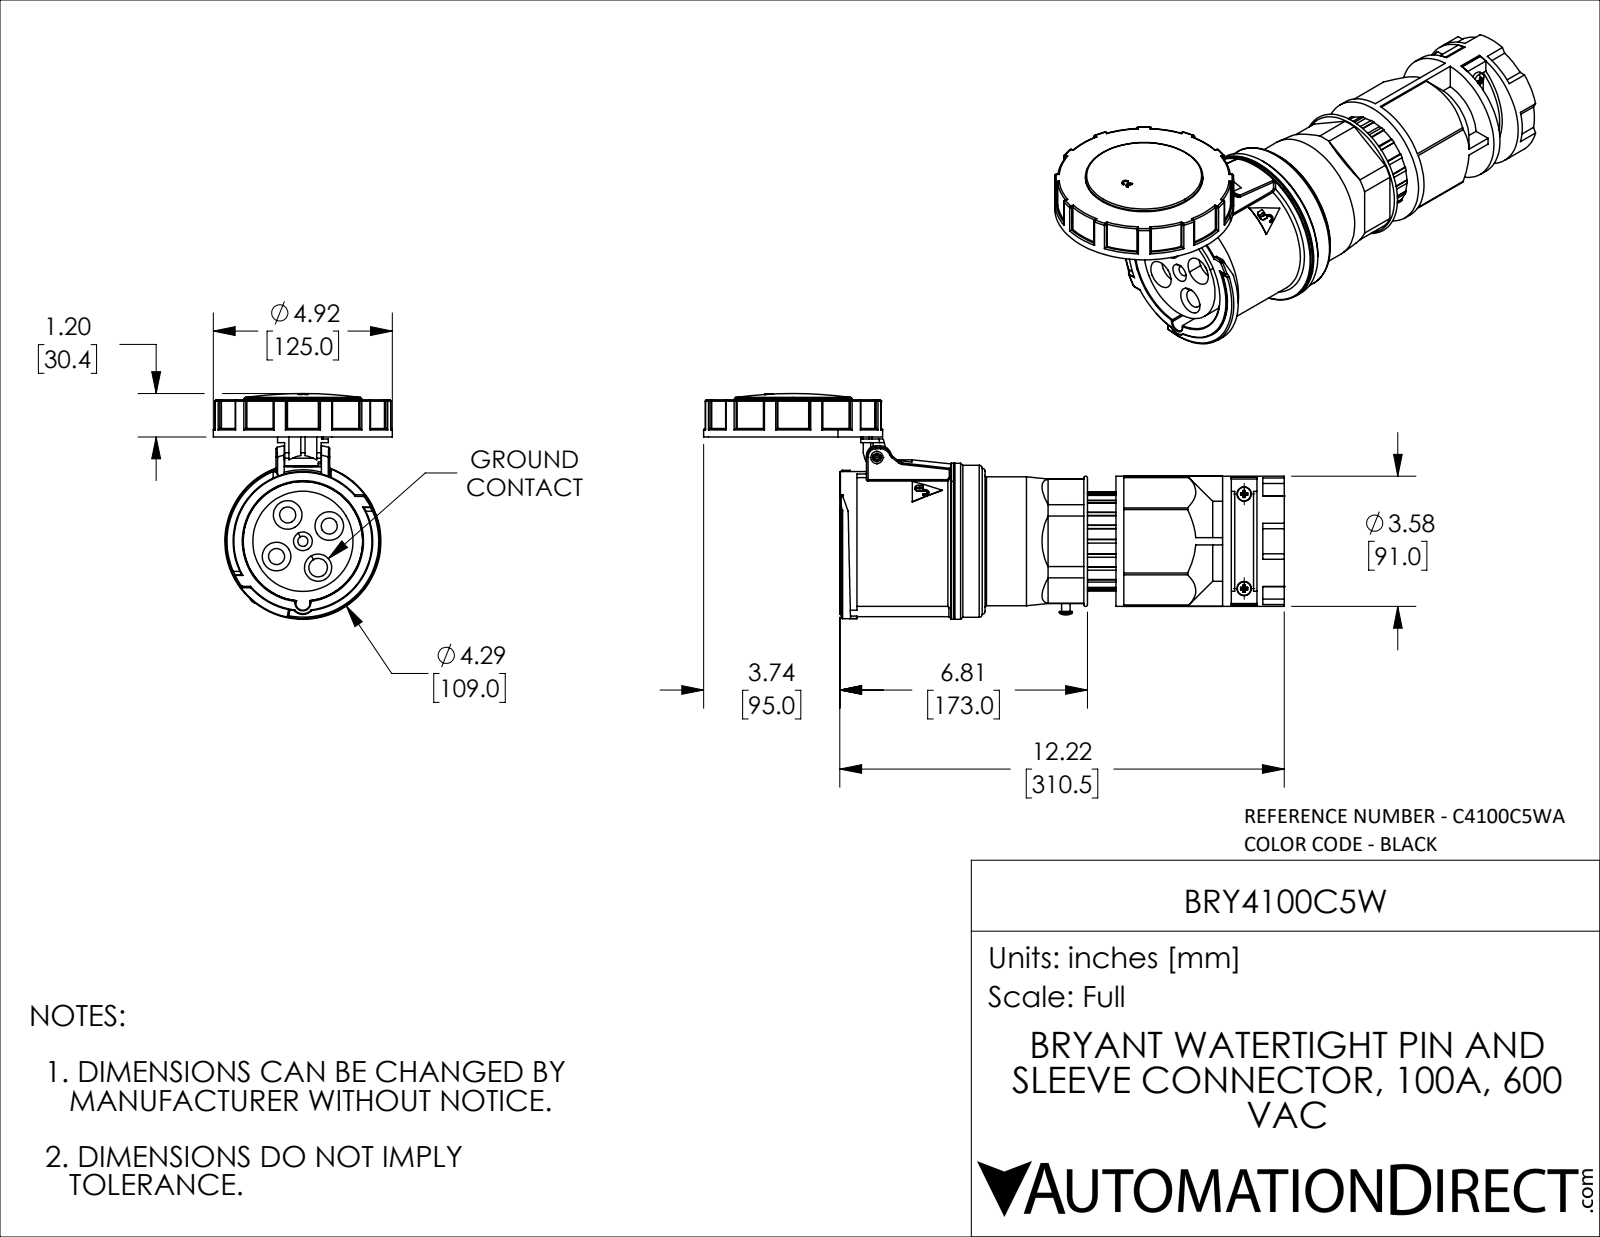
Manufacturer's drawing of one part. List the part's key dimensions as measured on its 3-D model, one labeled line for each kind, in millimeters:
Part name (STEP PRODUCT): BRY4100C5W
STEP written by: SolidWorks 2021 (CONFIG_CONTROL_DESIGN)
Units: millimetres
Bodies: 7 solids, 1107 faces (394 planar, 380 cylindrical, 333 other)
Overall size (bounding box): 405.5 × 157.65 × 125
Volume: 1 715 000 mm³ · Surface area: 254 576 mm²
Round holes (diameter × count): ⌀11.2 ×3, ⌀20 ×3, ⌀7.1 ×1, ⌀8.5 ×1, ⌀13 ×1, ⌀50 ×1, ⌀81 ×1, ⌀115 ×1
Round bosses / shafts (diameter × count): ⌀5 ×3, ⌀125 ×1, ⌀109 ×1, ⌀106.1 ×1, ⌀97.5 ×1, ⌀92.6 ×1, ⌀91 ×1, ⌀90 ×1
Partial cylindrical surfaces — rounded edges, fillets, slot ends (radius × count): R1 ×75, R0.5 ×5, R2 ×4, R3 ×4, R1.75 ×2, R2.5 ×2, R2.55 ×2, R2.6 ×2
Main face-to-face distances: 79.5, 100.5, 118.5, 18, 2.5, 23, 3, 27, 21, 24
Hole centre spacings: 21.24, 30.04, 42.49
